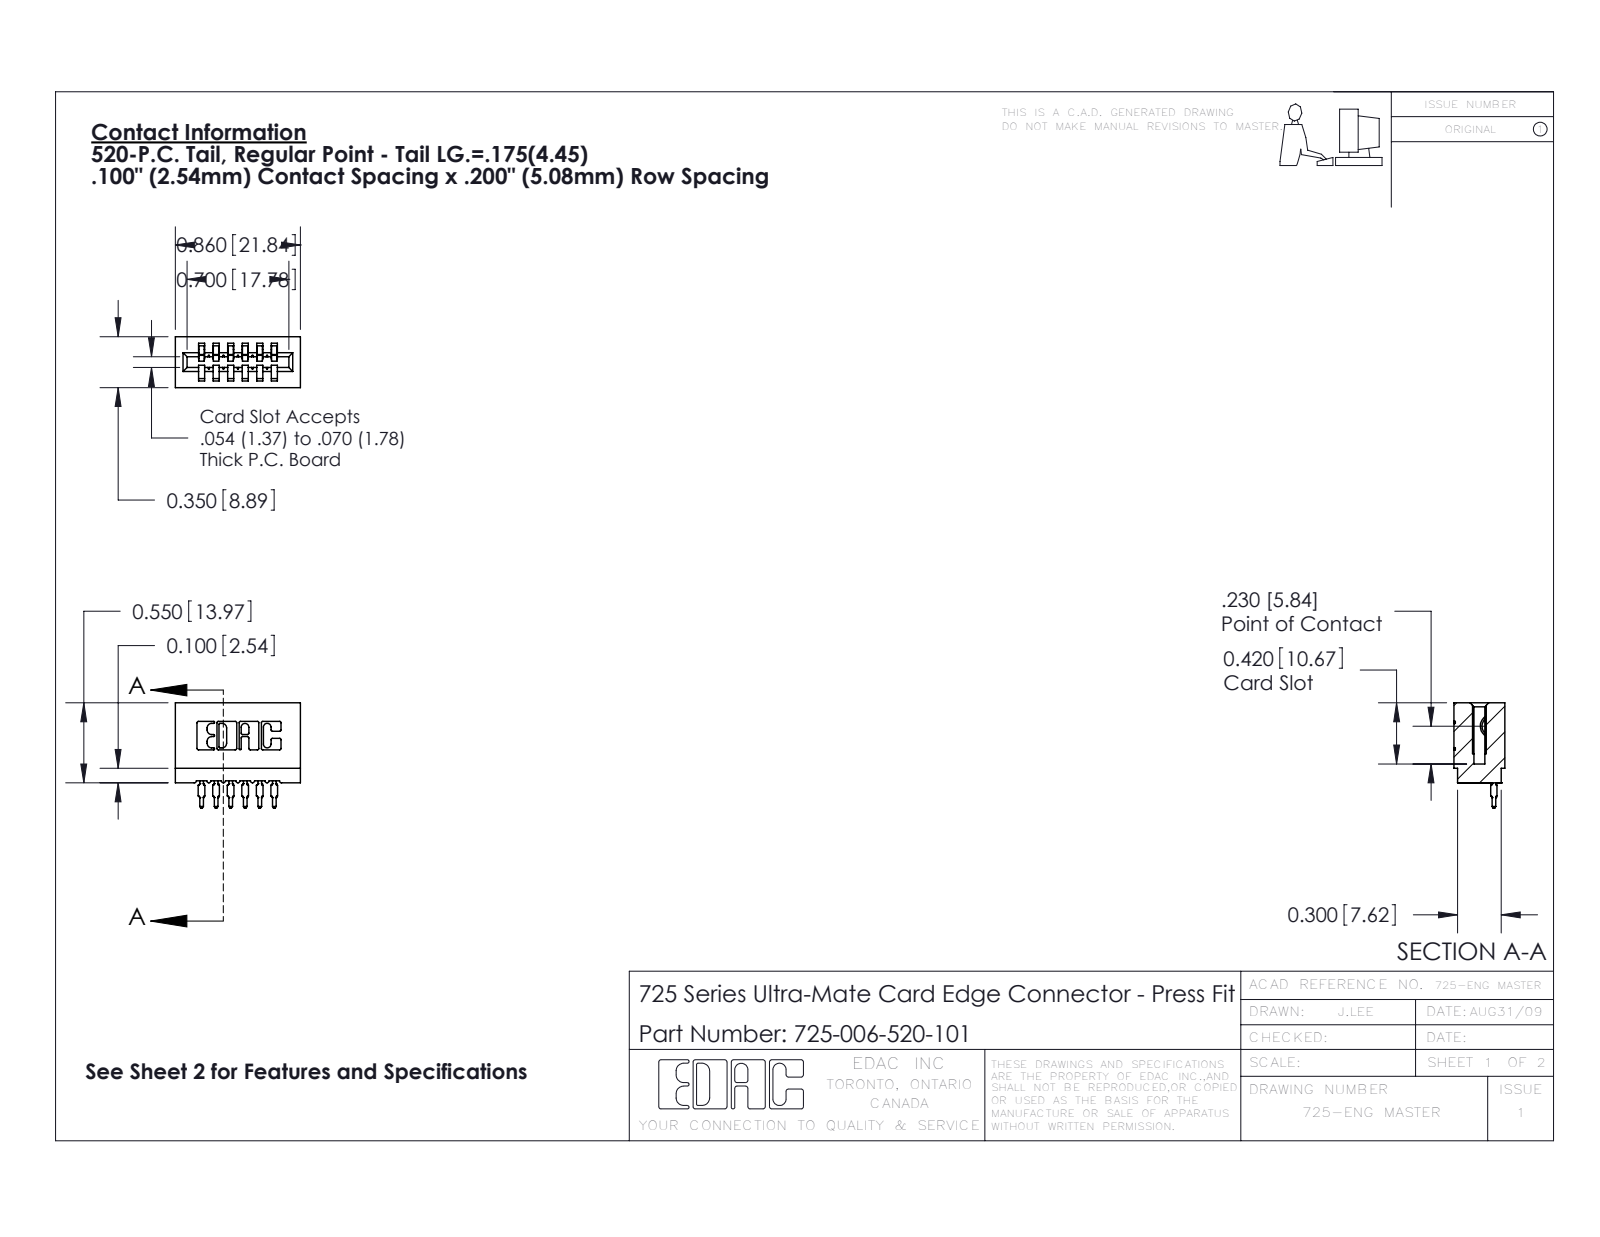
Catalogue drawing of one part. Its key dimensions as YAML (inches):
part_name: "745-292-001_520; 725 Part_Insulator Option - 01; 725-006-520-101"
step_written_by: "SolidWorks 2016 (CONFIG_CONTROL_DESIGN)"
units: inches
bodies: {solids: 7, faces: 767, planar: 457, cylindrical: 154, other: 156}
overall_size: [0.86, 0.725, 0.35]
volume: 0.113
surface_area: 4.446
partial_cylinders:
  - {radius: 0.01, count: 22}
  - {radius: 0.015, count: 12}
  - {radius: 0.021, count: 12}
  - {radius: 0.007, count: 6}
  - {radius: 0.031, count: 6}
  - {radius: 0.005, count: 4}
  - {radius: 0.011, count: 4}
  - {radius: 0.026, count: 3}
face_to_face_distances: [0.1, 0.2, 0.042, 0.3, 0.058, 0.142, 0.158, 0.242, 0.4, 0.35]
